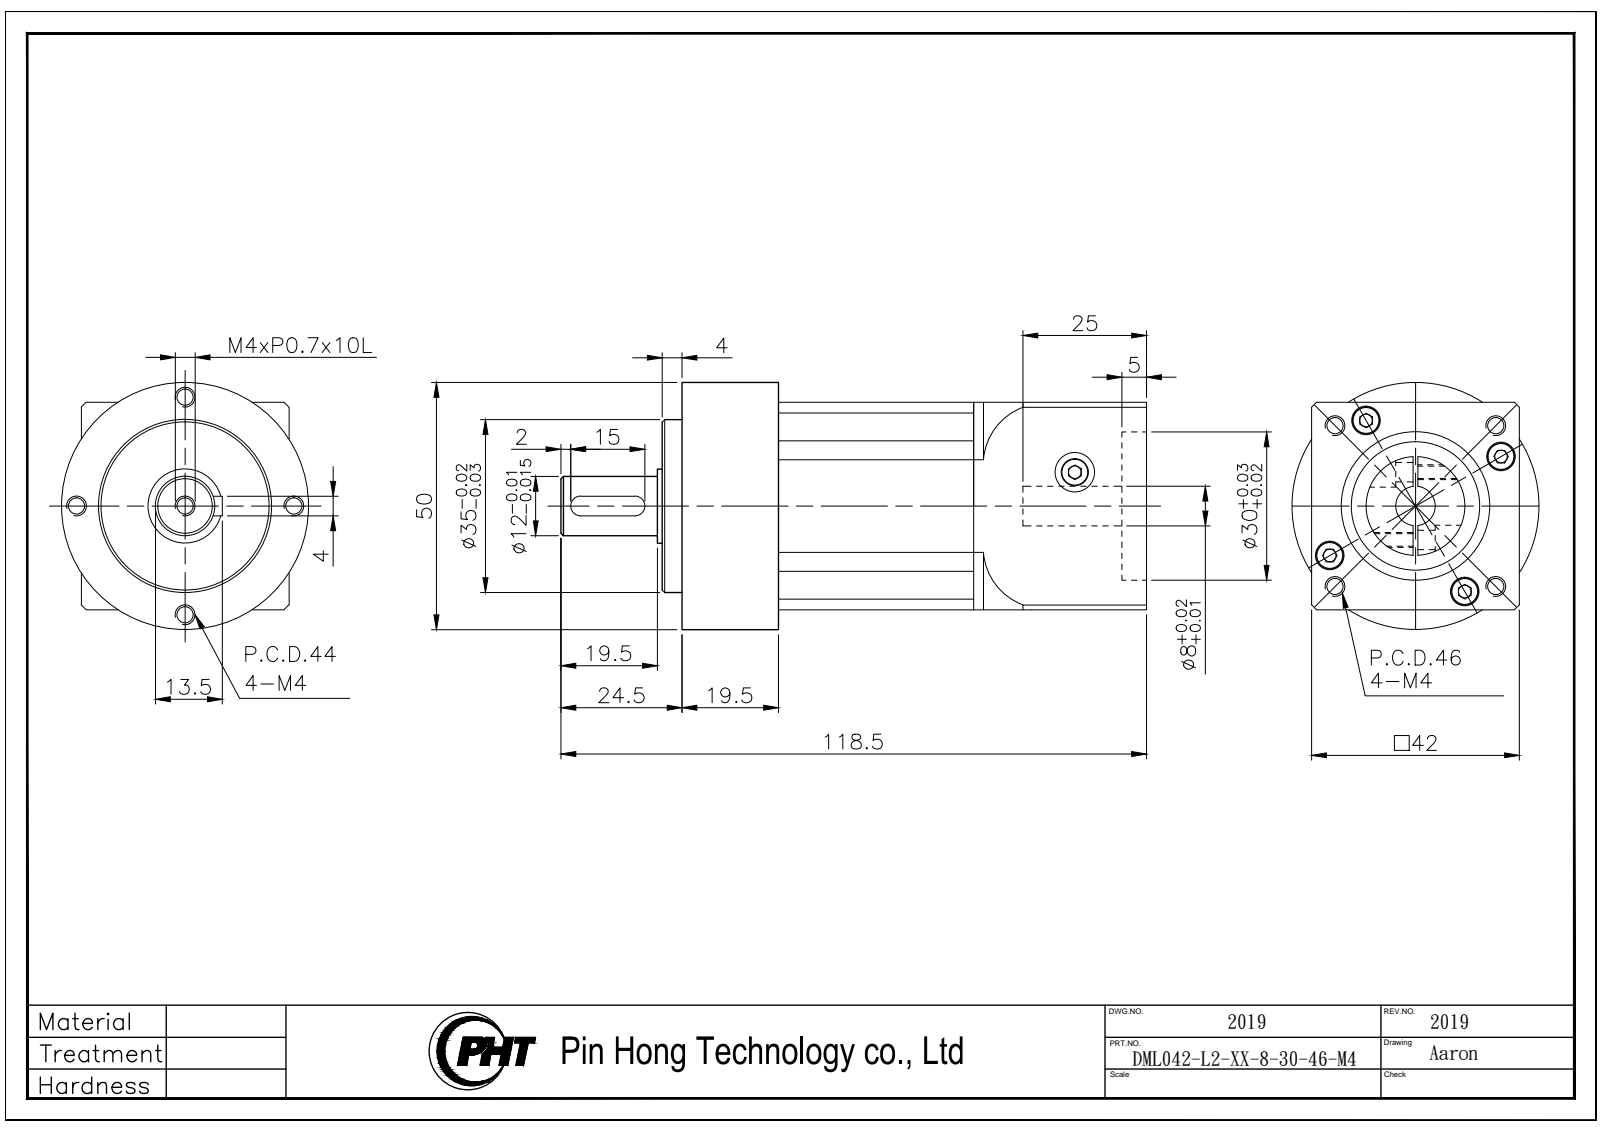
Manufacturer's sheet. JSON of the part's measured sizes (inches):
{"part_name": "DML042-L2-XX-8-30-46-M4_2019", "step_written_by": "SolidWorks 2016 (AUTOMOTIVE_DESIGN)", "units": "inches", "bodies": {"solids": 3, "faces": 189, "planar": 68, "cylindrical": 89, "other": 32}, "overall_size": [4.665, 1.969, 1.969], "volume_in3": 9.147, "surface_area_in2": 53.09, "round_holes": [[0.13, 13], [0.228, 4], [0.315, 3], [1.024, 1], [1.181, 1]], "round_bosses_or_shafts": [[0.217, 4], [1.969, 1], [1.378, 1], [0.787, 1], [0.591, 1], [0.472, 1]], "partial_cylinders_radius": [[0.157, 4], [0.079, 2], [0.906, 1], [1.142, 1]], "face_to_face_distances": [1.654, 1.555, 0.768, 3.701, 2.323, 1.378, 2.933, 0.157, 3.858, 2.48], "hole_center_spacings": [0.679, 1.637, 0.25, 0.435, 0.787, 0.83, 0.866, 0.906]}
